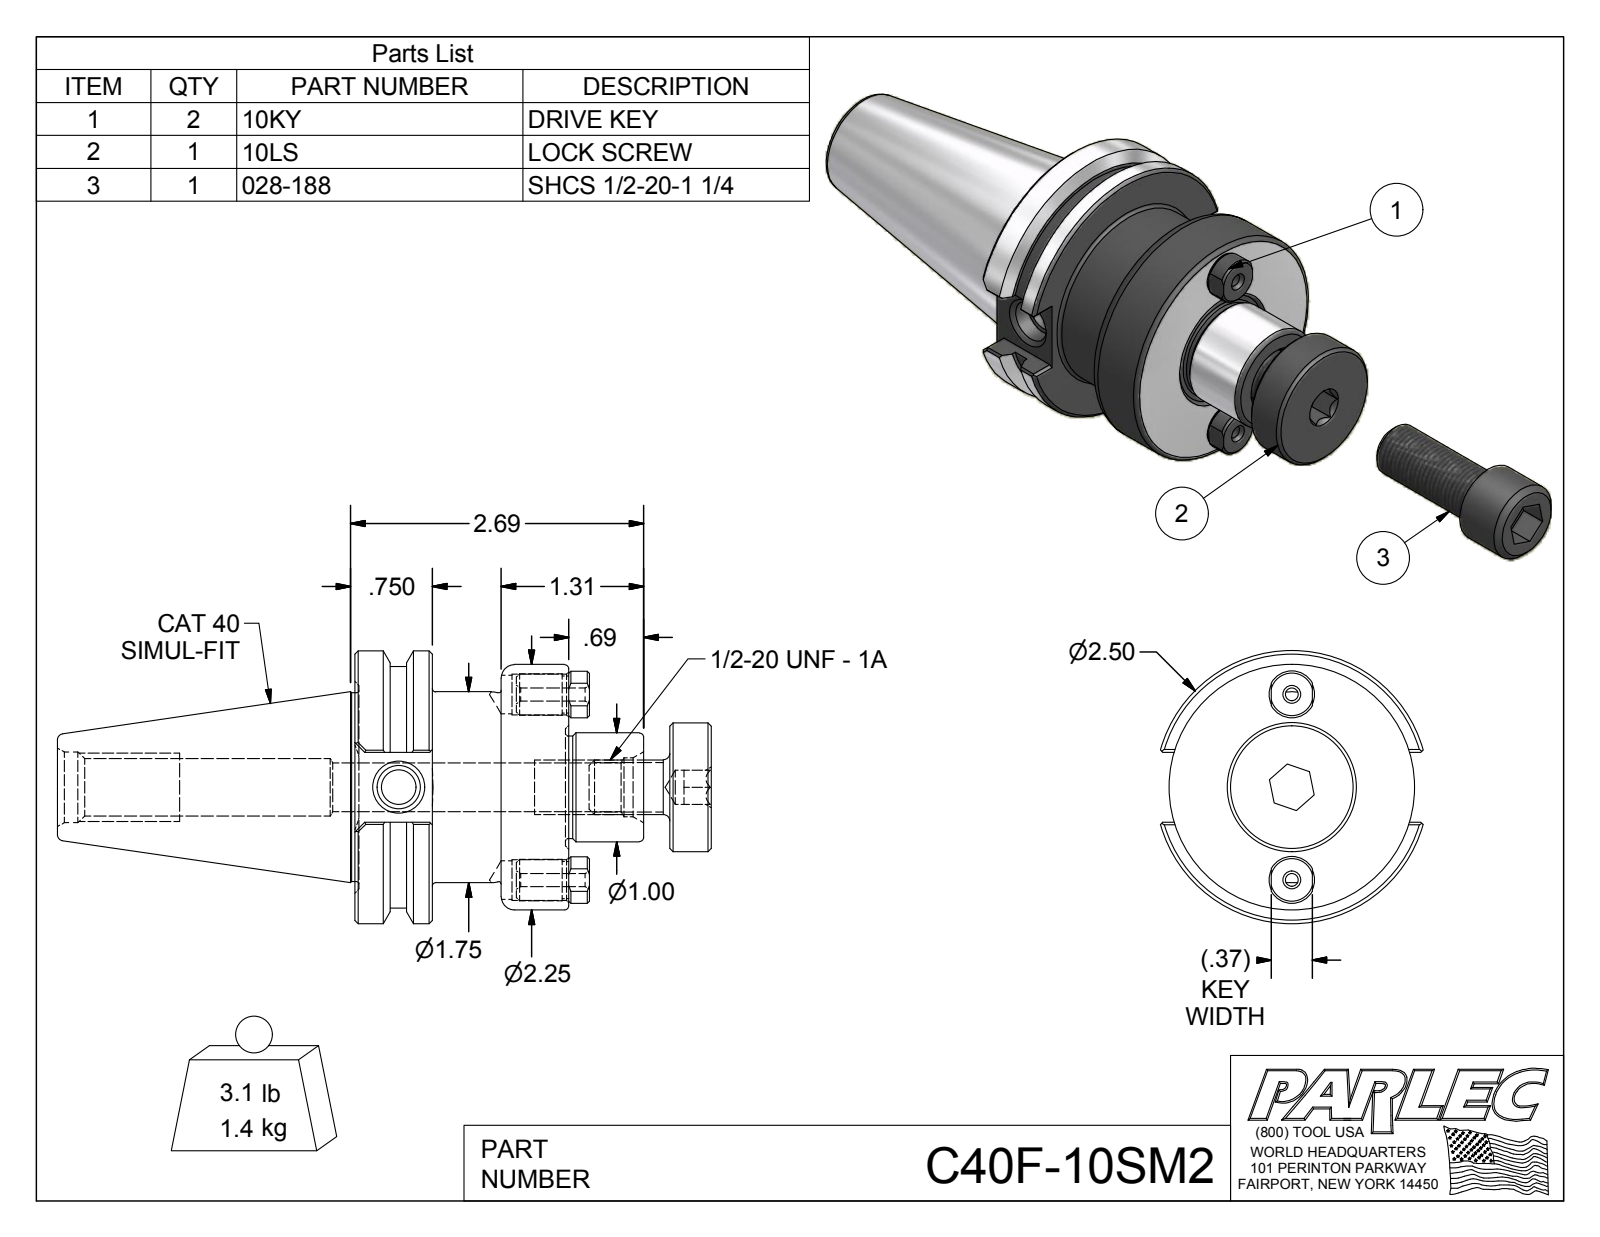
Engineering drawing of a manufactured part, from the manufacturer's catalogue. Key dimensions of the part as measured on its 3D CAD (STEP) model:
Part name (STEP PRODUCT): C40F-10SM2; C40F-10SM2-1; 10KY; 028-188 (+1 more)
STEP written by: Autodesk Inventor 2012 (AUTOMOTIVE_DESIGN)
Units: inches
Bodies: 5 solids, 165 faces (70 planar, 36 cylindrical, 59 other)
Overall size (bounding box): 8.621 × 2.5 × 2.406
Volume: 11.42 in³ · Surface area: 59.99 in²
Round holes (diameter × count): ⌀0.12 ×2, ⌀0.354 ×2, ⌀0.374 ×2, ⌀0.312 ×1, ⌀0.315 ×1, ⌀0.399 ×1, ⌀0.446 ×1, ⌀0.527 ×1, ⌀0.54 ×1, ⌀0.648 ×1
Round bosses / shafts (diameter × count): ⌀0.38 ×2, ⌀0.34 ×2, ⌀2.5 ×1, ⌀2.25 ×1, ⌀2.215 ×1, ⌀1.75 ×1, ⌀1.73 ×1, ⌀1.18 ×1
Partial cylindrical surfaces — rounded edges, fillets, slot ends (radius × count): R0.214 ×2
Main face-to-face distances: 1.25, 0.711, 1.961, 1.307, 3.268, 2.557, 0.62, 2.888, 2.177, 0.927
Hole centre spacings: 0.85, 1.7
